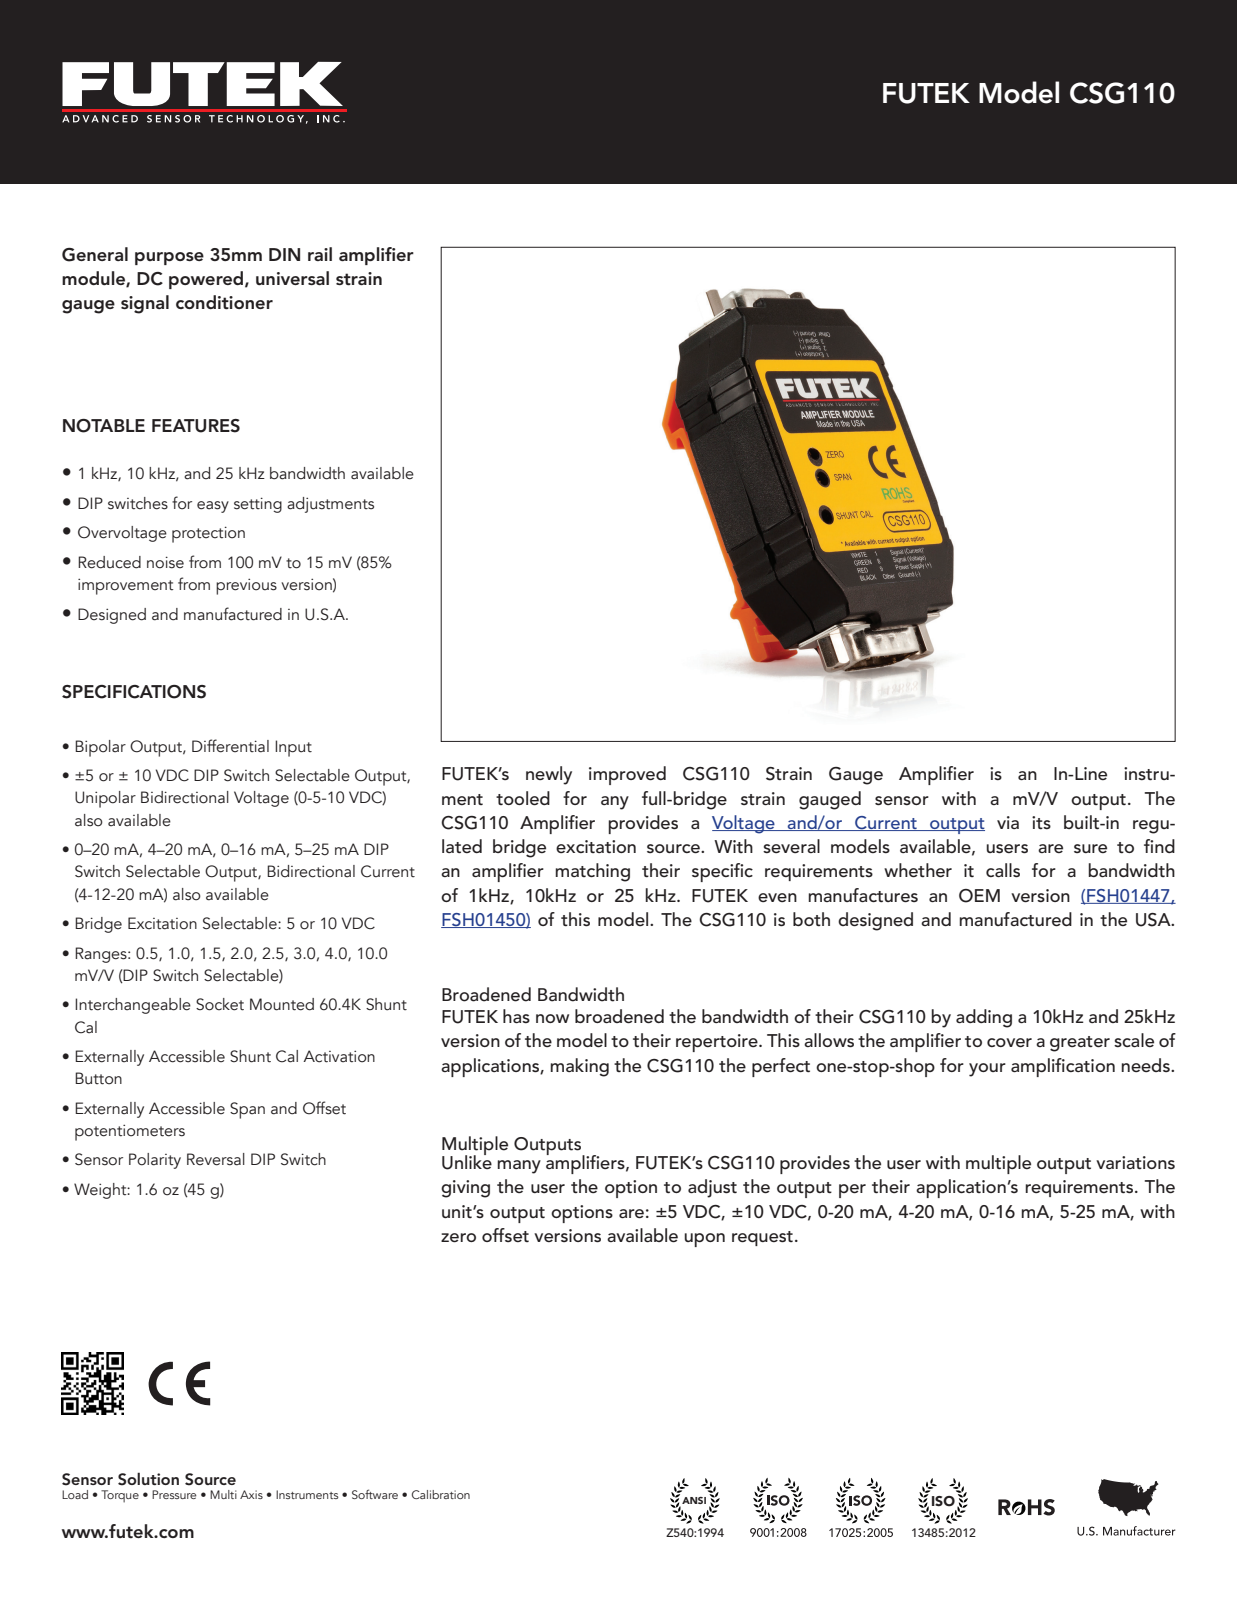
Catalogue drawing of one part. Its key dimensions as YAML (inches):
part_name: "CSG110; JM2; DP9MALE; DP9FEMALE (+3 more)"
step_written_by: "Mechanical Desktop 2008 (CONFIG_CONTROL_DESIGN)"
units: inches
bodies: {solids: 5, faces: 338, planar: 173, cylindrical: 142, other: 23}
overall_size: [3.086, 1.67, 1.492]
volume: 3.794
surface_area: 31.6
round_holes:
  - {diameter: 0.042, count: 9}
  - {diameter: 0.109, count: 3}
  - {diameter: 0.08, count: 2}
  - {diameter: 0.112, count: 2}
  - {diameter: 0.05, count: 1}
round_bosses_or_shafts:
  - {diameter: 0.04, count: 9}
  - {diameter: 0.293, count: 1}
partial_cylinders:
  - {radius: 0.05, count: 26}
  - {radius: 0.02, count: 14}
  - {radius: 0.1, count: 8}
  - {radius: 0.015, count: 4}
  - {radius: 0.03, count: 4}
  - {radius: 0.082, count: 4}
face_to_face_distances: [0.83, 0.867, 0.037, 1.67, 2.53, 0.953, 0.123, 0.086, 1.297, 0.467]
hole_center_spacings: [0.161, 0.115, 0.229, 0.23, 0.324, 0.345, 0.094, 0.137]
